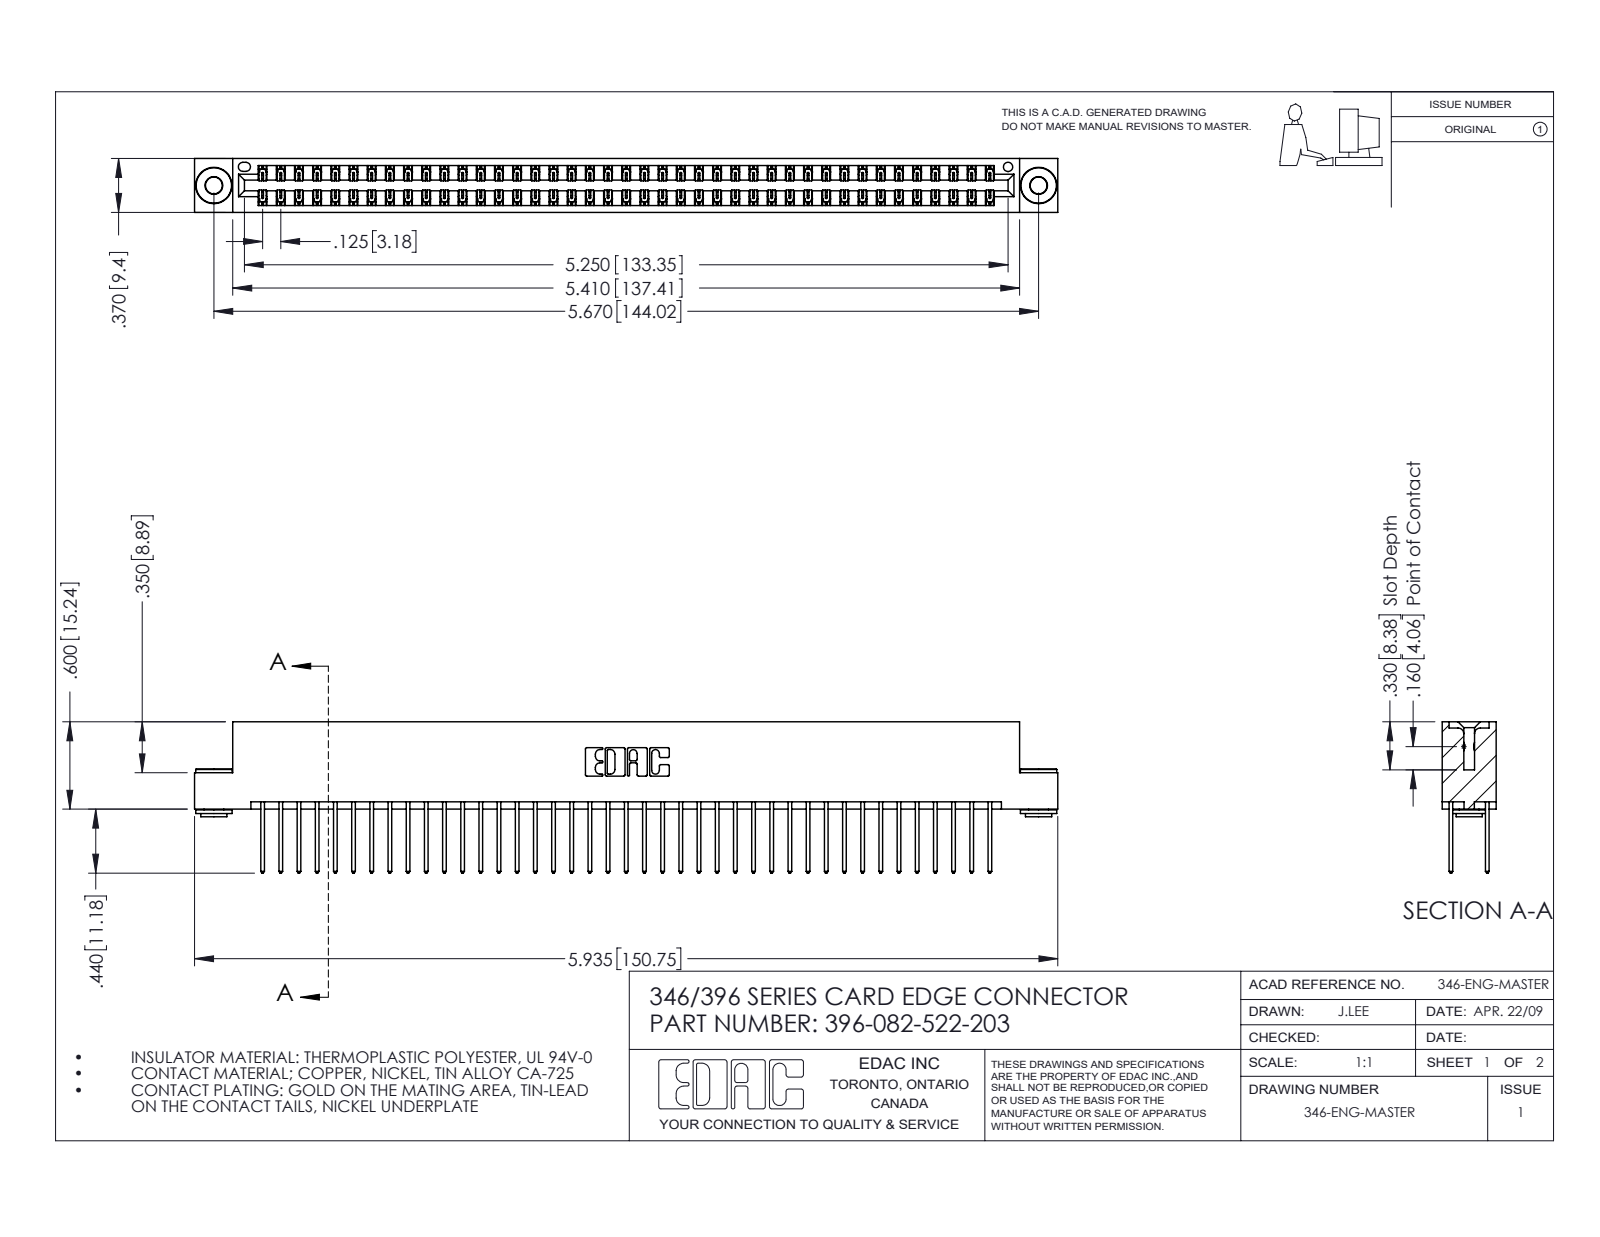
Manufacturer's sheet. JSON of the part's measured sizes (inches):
{"part_name": "345-292-001_345-293-122; 396-082-522-203; 345-250-002_345-250-002-102; 346 Part_Flush Mounting Lugs - 0.156 Dia-TH", "step_written_by": "SolidWorks 2016 (CONFIG_CONTROL_DESIGN)", "units": "inches", "bodies": {"solids": 85, "faces": 4424, "planar": 2956, "cylindrical": 1460, "other": 8}, "overall_size": [5.935, 1.04, 0.37], "volume_in3": 0.911, "surface_area_in2": 33.61, "round_holes": [[0.116, 2], [0.156, 2], [0.064, 1]], "round_bosses_or_shafts": [[0.25, 2], [0.18, 2], [0.136, 2]], "partial_cylinders_radius": [[0.006, 123], [0.01, 82], [0.01, 22], [0.007, 6], [0.031, 6], [0.026, 3], [0.014, 2], [0.022, 2]], "face_to_face_distances": [0.048, 0.322, 0.25, 0.025, 0.37, 0.072, 0.298, 0.275, 0.148, 0.222], "hole_center_spacings": [0.246, 5.461, 5.67]}
